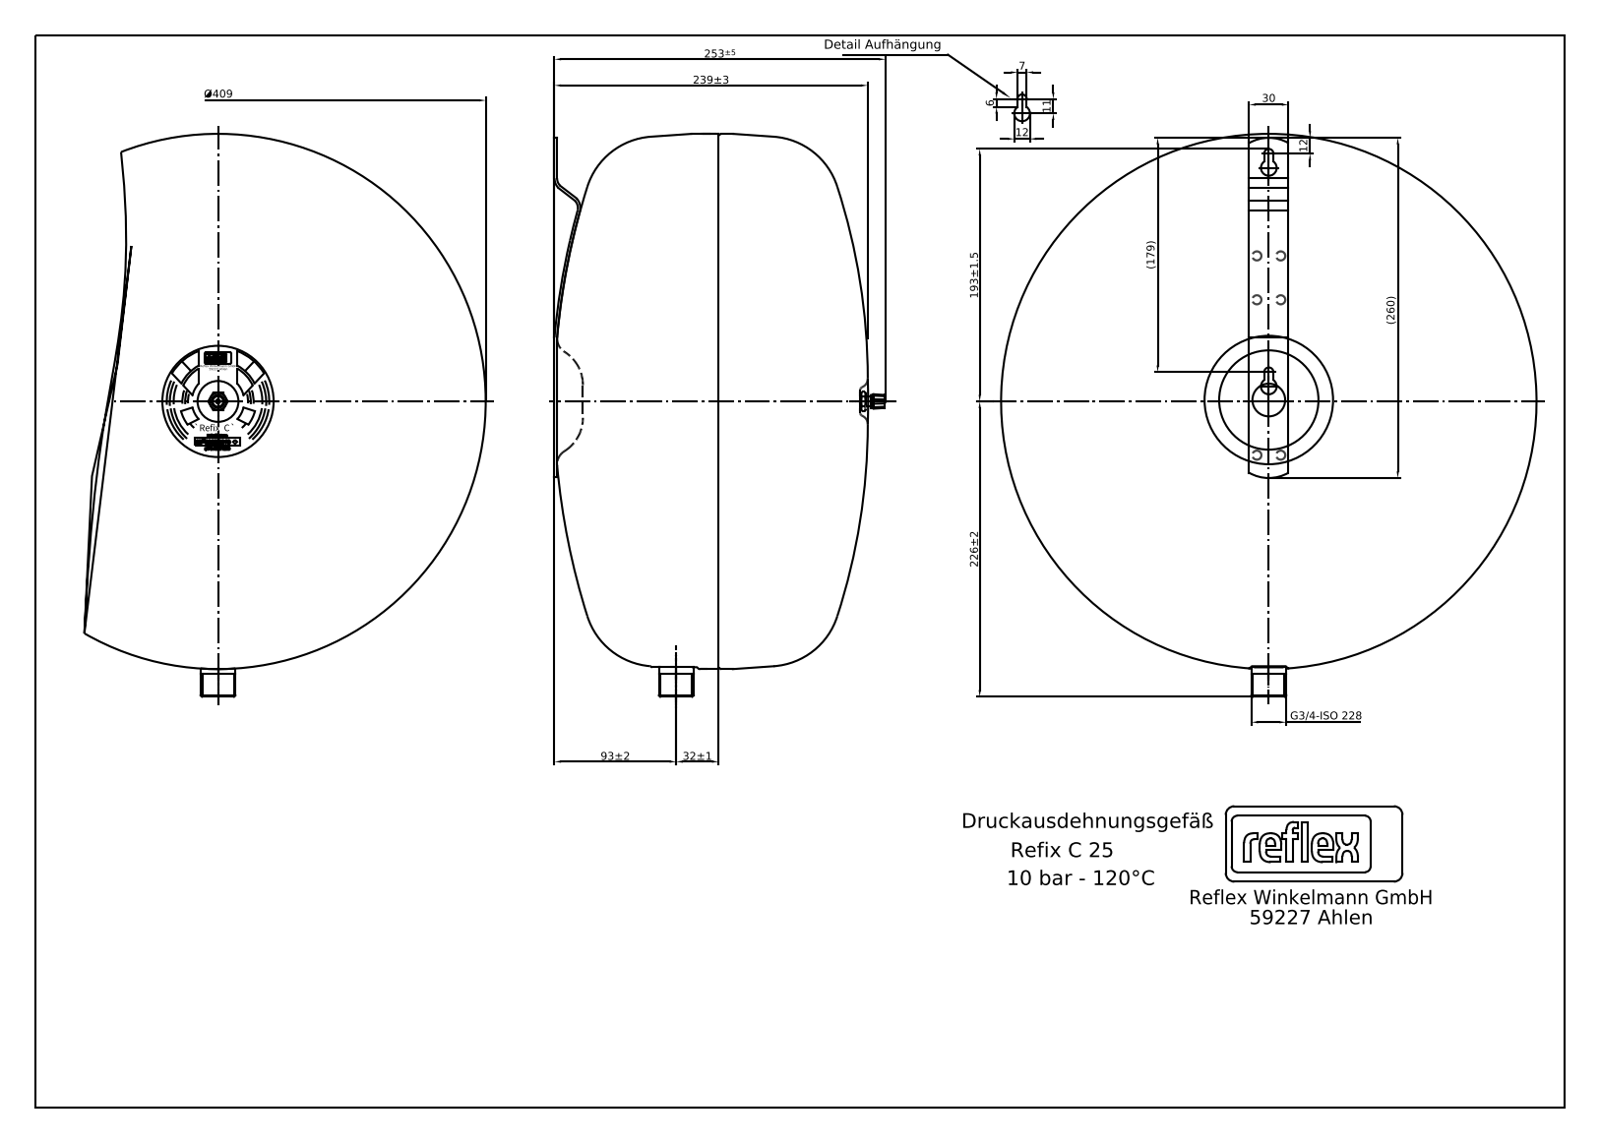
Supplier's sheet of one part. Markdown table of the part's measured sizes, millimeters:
| quantity | value |
| --- | --- |
| STEP written by | Mechanical Desktop 2011 (CONFIG_CONTROL_DESIGN) |
| units | millimeters |
| bodies | 10 solids, 146 faces (74 planar, 46 cylindrical, 26 other) |
| overall size | 429 × 406 × 240.51 |
| volume | 25 250 000 mm³ |
| surface area | 469 452 mm² |
| round holes (diameter × count) | 12 × 2 |
| round bosses / shafts (diameter × count) | 406 × 1, 26 × 1, 15 × 1, 11 × 1, 8 × 1 |
| partial cylindrical surfaces (radius × count) | 1.41 × 4, 0.56 × 3, 0.96 × 2, 1.69 × 2, 2.32 × 2, 2.35 × 2, 3.18 × 2, 3.5 × 2 |
| main face-to-face distances | 2, 20.1, 22.1, 23, 30, 198, 218.1, 220.1, 20.12, 218.12 |
| hole center spacings | 167 |
